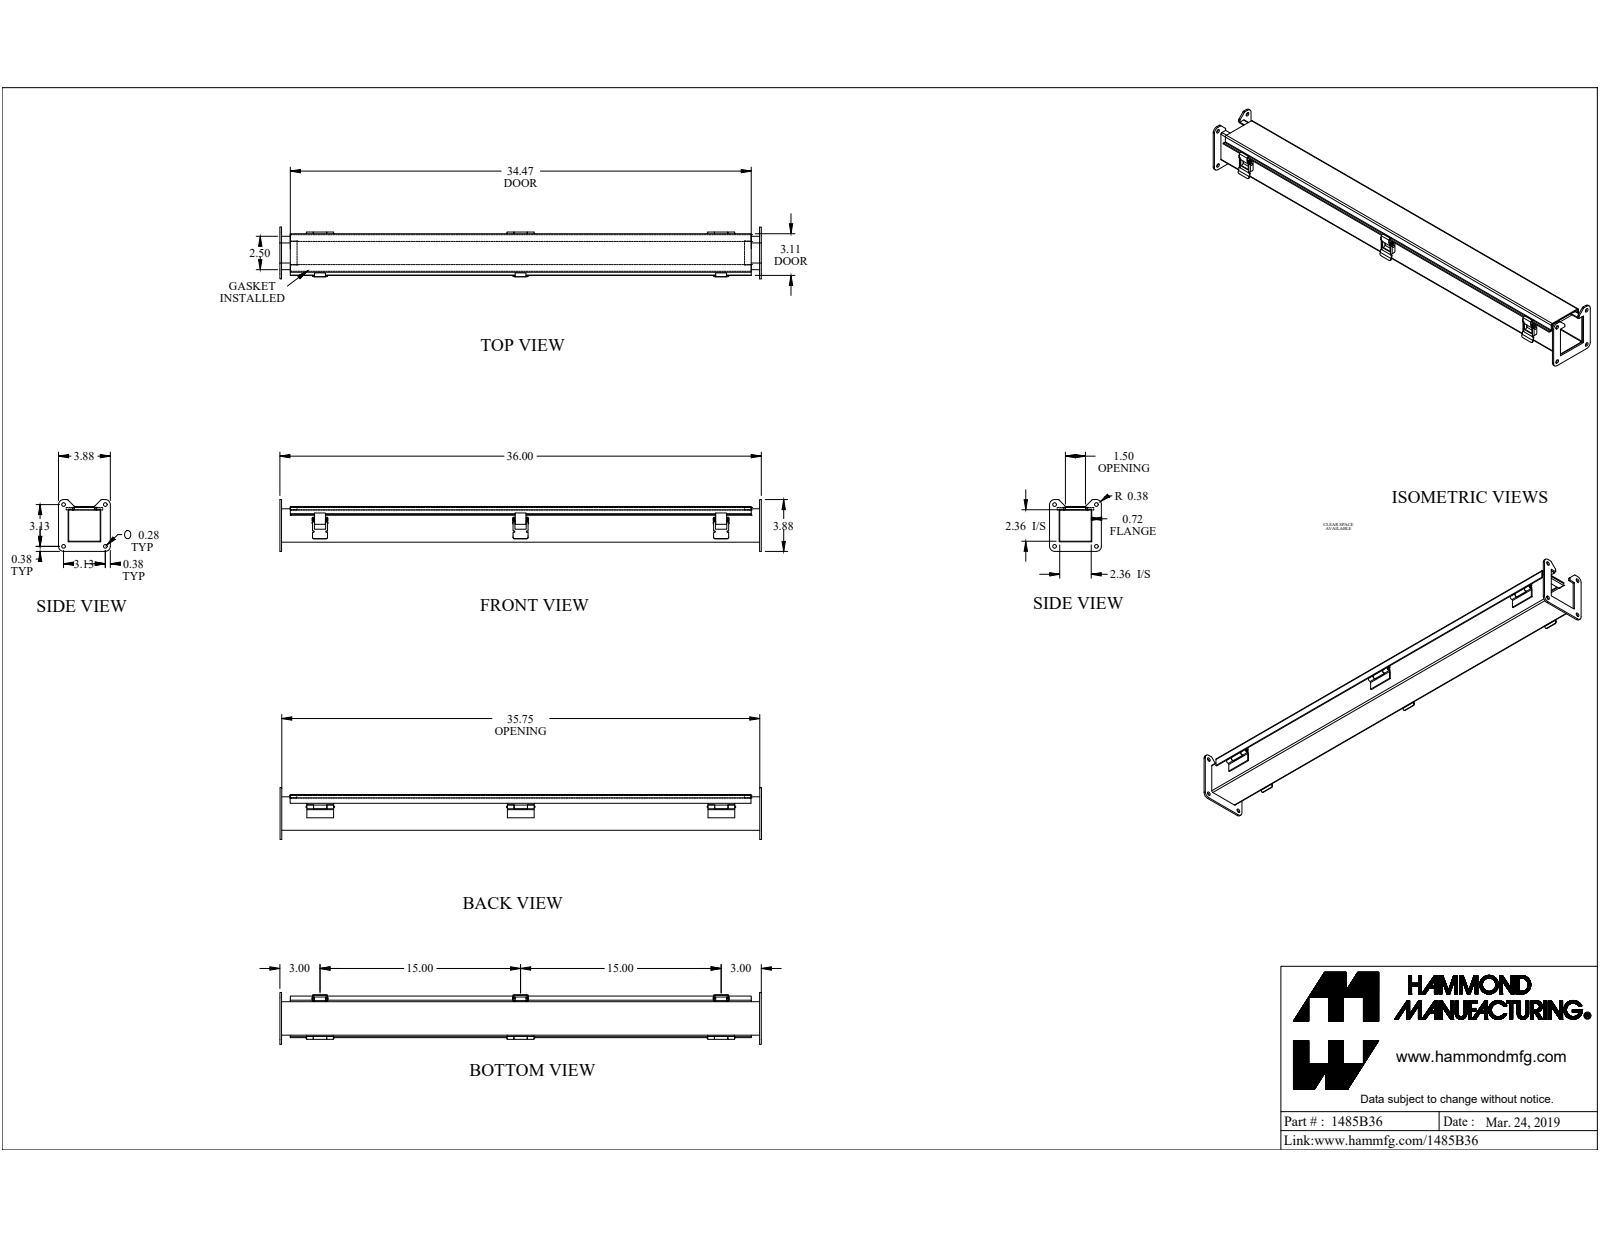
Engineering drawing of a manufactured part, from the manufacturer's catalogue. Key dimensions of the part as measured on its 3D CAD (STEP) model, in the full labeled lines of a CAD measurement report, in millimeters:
Part name (STEP PRODUCT): 1485B36
STEP written by: SolidWorks 2019 (CONFIG_CONTROL_DESIGN)
Units: millimetres
Bodies: 26 solids, 510 faces (304 planar, 188 cylindrical, 18 other)
Overall size (bounding box): 914.4 × 98.4 × 98.4
Volume: 678 900 mm³ · Surface area: 691 600 mm²
Round holes (diameter × count): ⌀7.1 ×4, ⌀3.2 ×1, ⌀4.2 ×1
Round bosses / shafts (diameter × count): ⌀7 ×1, ⌀4.1 ×1, ⌀4 ×1, ⌀3.2 ×1, ⌀3.2 ×1
Partial cylindrical surfaces — rounded edges, fillets, slot ends (radius × count): R0.7 ×12, R2.2 ×12, R3.2 ×11, R0.9 ×7, R2.7 ×7, R0.4 ×6, R1.2 ×6, R9.5 ×4
Main face-to-face distances: 1.8, 61.7, 66, 63.5, 59.8, 67.9, 64.2, 4.4, 66.4, 4.7
Hole centre spacings: 79.4, 112.3, 27.3, 27.9, 51.5, 52.4, 74.3, 80.6
